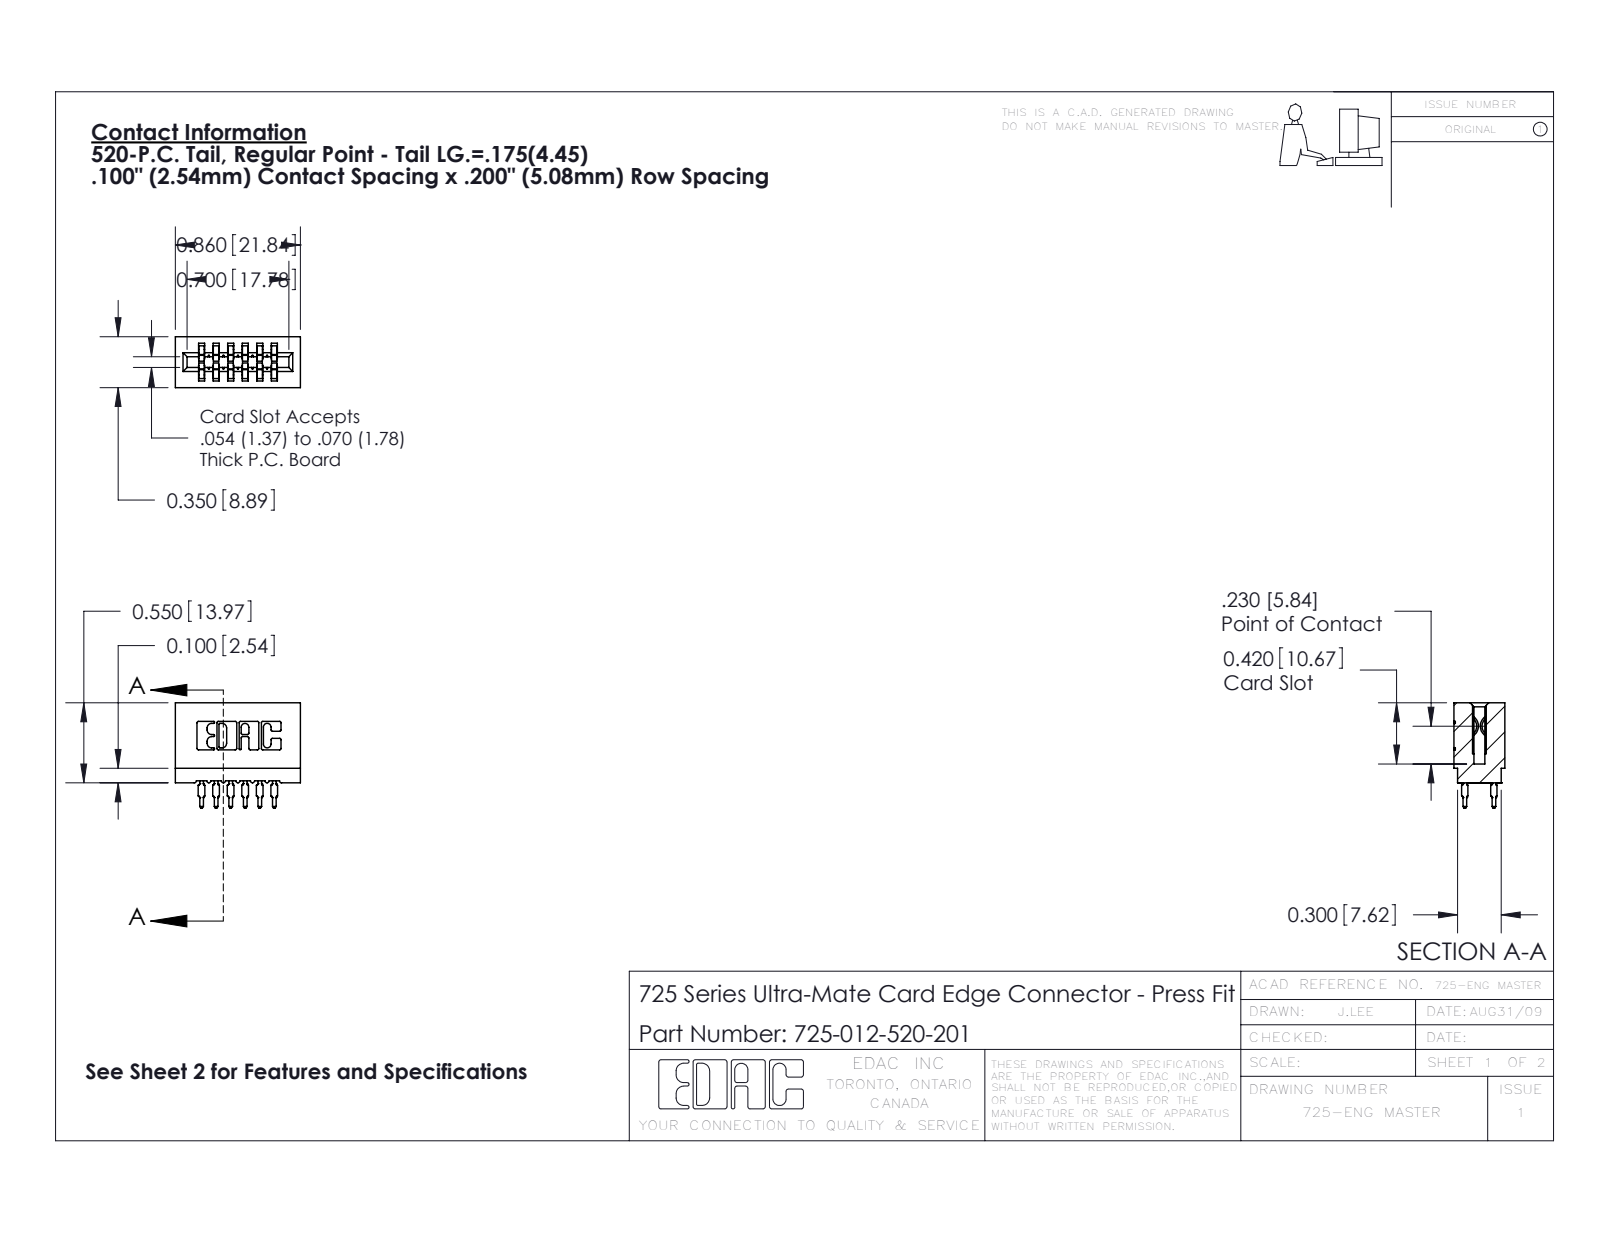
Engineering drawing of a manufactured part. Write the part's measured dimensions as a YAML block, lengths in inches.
part_name: "725-012-520-201; 745-292-001_520; 725 Part_Insulator Option - 01"
step_written_by: "SolidWorks 2016 (CONFIG_CONTROL_DESIGN)"
units: inches
bodies: {solids: 13, faces: 1169, planar: 607, cylindrical: 250, other: 312}
overall_size: [0.86, 0.725, 0.35]
volume: 0.116
surface_area: 4.941
partial_cylinders:
  - {radius: 0.021, count: 24}
  - {radius: 0.01, count: 22}
  - {radius: 0.015, count: 12}
  - {radius: 0.005, count: 8}
  - {radius: 0.011, count: 8}
  - {radius: 0.007, count: 6}
  - {radius: 0.031, count: 6}
  - {radius: 0.026, count: 3}
face_to_face_distances: [0.1, 0.2, 0.3, 0.042, 0.142, 0.058, 0.4, 0.242, 0.158, 0.35]
